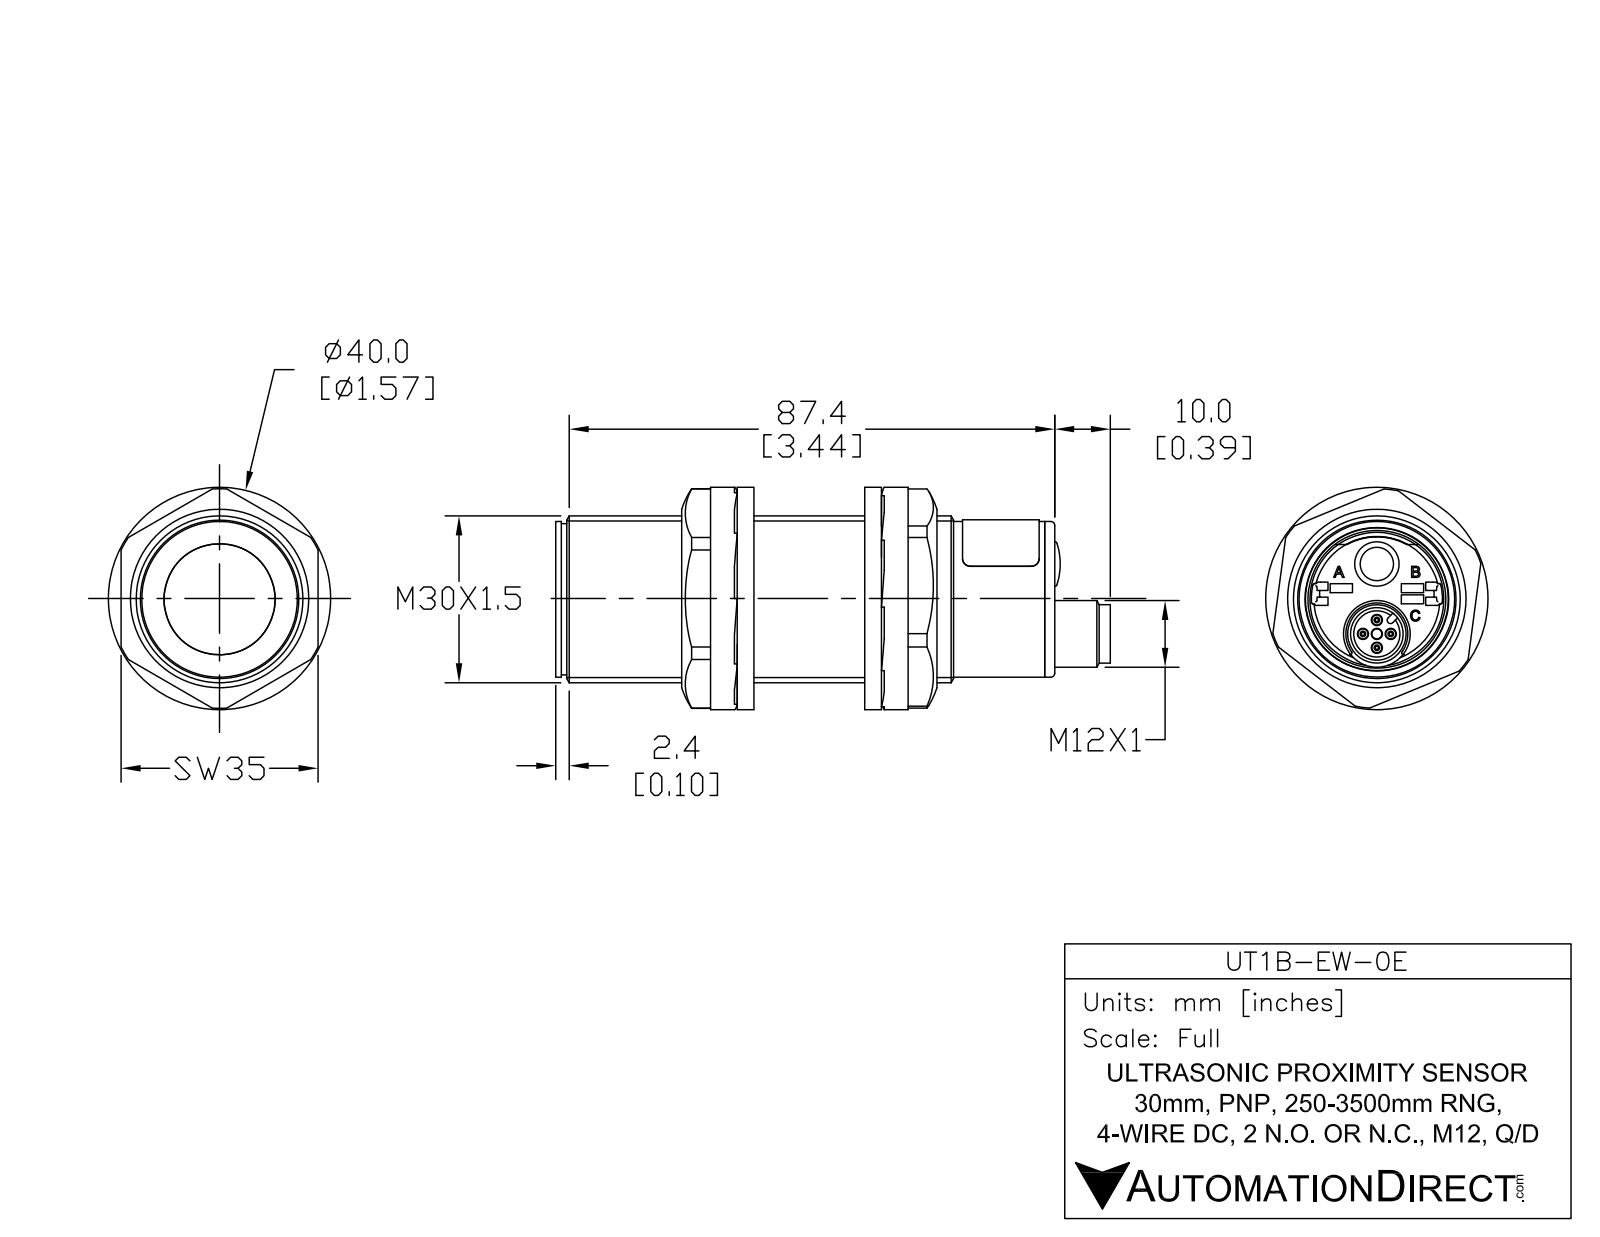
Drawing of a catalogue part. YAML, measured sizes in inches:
part_name: "UT1B-EW-0E"
step_written_by: "SolidWorks 2017 (AUTOMOTIVE_DESIGN)"
units: inches
bodies: {solids: 5, faces: 107, planar: 30, cylindrical: 45, other: 32}
overall_size: [3.89, 1.181, 1.181]
volume: 3.754
surface_area: 20.71
round_holes:
  - {diameter: 0.071, count: 4}
  - {diameter: 0.315, count: 1}
  - {diameter: 0.327, count: 1}
  - {diameter: 0.372, count: 1}
  - {diameter: 0.925, count: 1}
round_bosses_or_shafts:
  - {diameter: 0.039, count: 4}
  - {diameter: 1.181, count: 1}
  - {diameter: 1.102, count: 1}
  - {diameter: 1.071, count: 1}
  - {diameter: 0.472, count: 1}
  - {diameter: 0.413, count: 1}
  - {diameter: 0.364, count: 1}
partial_cylinders:
  - {radius: 0.012, count: 2}
  - {radius: 0.024, count: 1}
face_to_face_distances: [3.386, 3.457, 0.039, 3.425, 0.071, 3.496, 0.039, 0.059, 3.425, 3.496]
hole_center_spacings: [0.098, 0.139, 0.197, 0.264, 0.505, 0.146, 0.245, 0.25]
